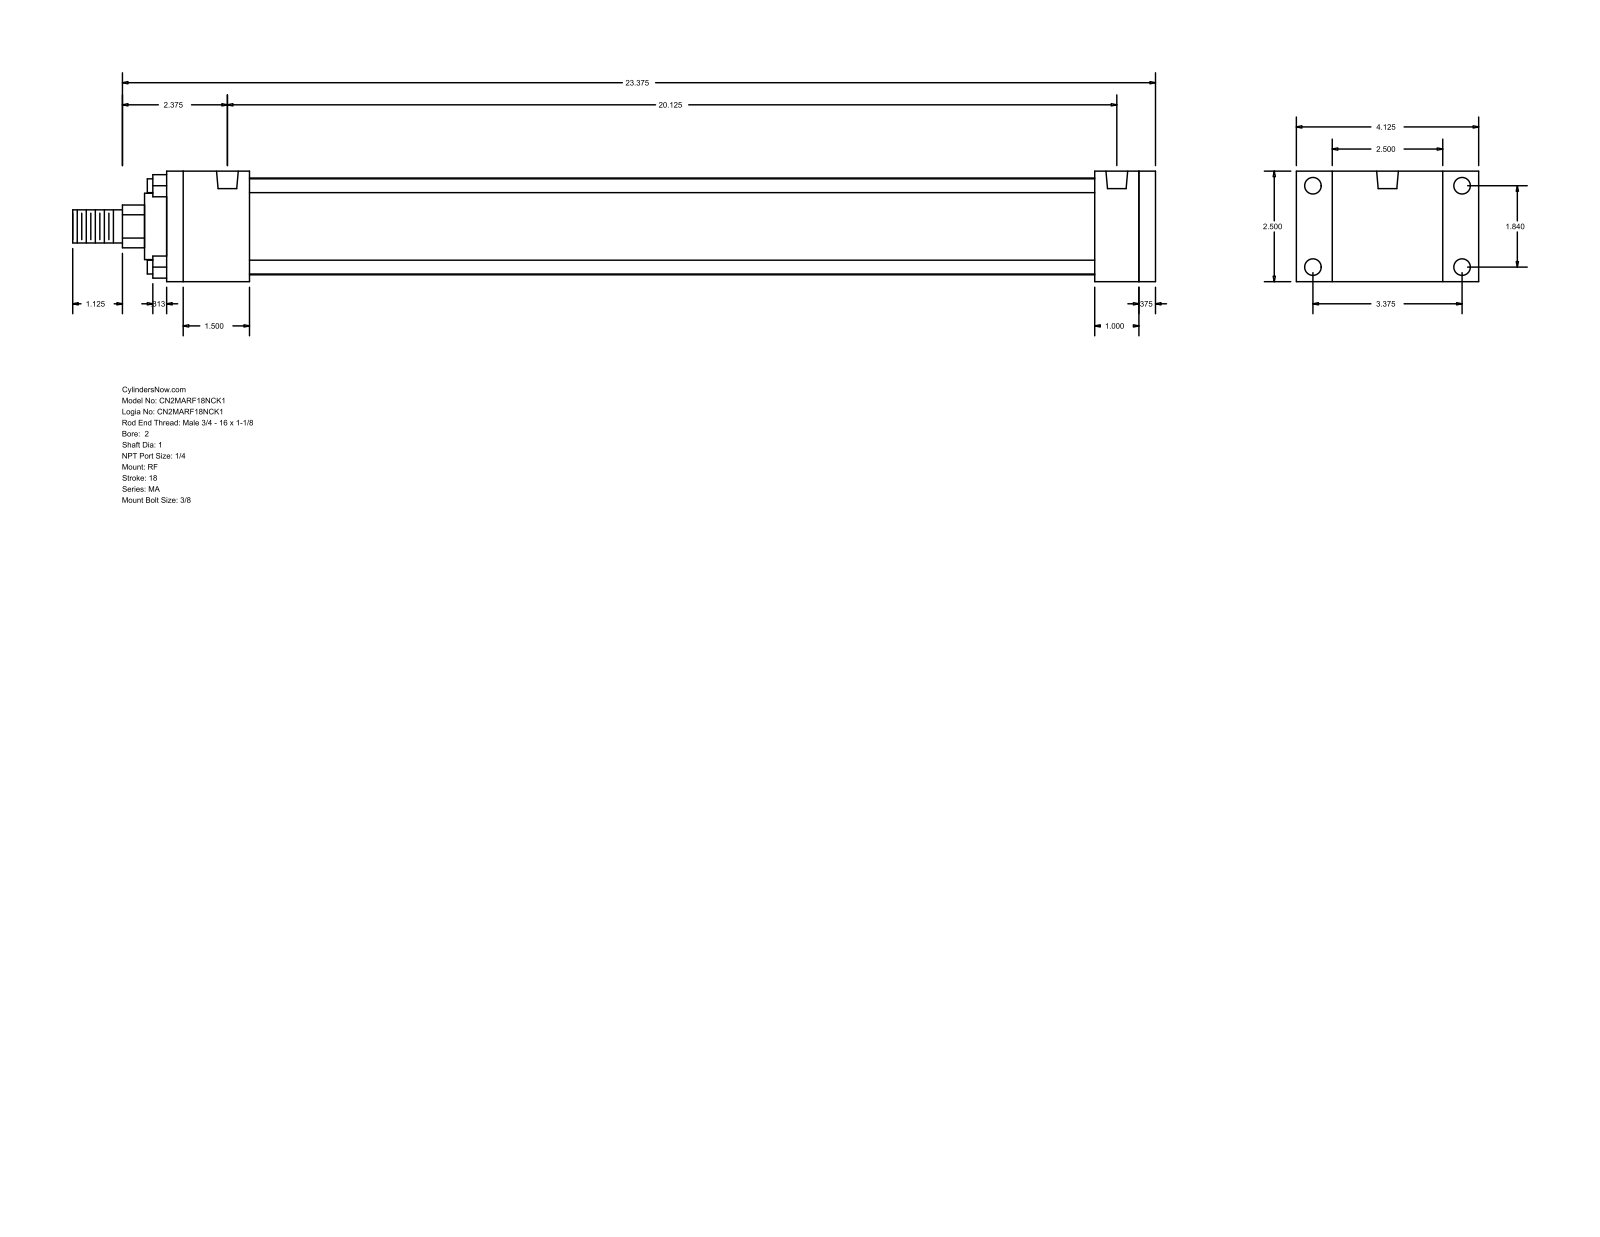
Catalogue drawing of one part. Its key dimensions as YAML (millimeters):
part_name: "MA_RF__0200_1"
step_written_by: "GSSL Pune (CONFIG_CONTROL_DESIGN)"
units: millimeters
bodies: {solids: 0, faces: 92, planar: 64, cylindrical: 28, other: 0}
overall_size: [622.3, 104.78, 63.5]
round_holes:
  - {diameter: 7.94, count: 4}
  - {diameter: 9.53, count: 4}
  - {diameter: 12.49, count: 2}
round_bosses_or_shafts:
  - {diameter: 7.94, count: 4}
  - {diameter: 55.63, count: 1}
  - {diameter: 38.1, count: 1}
  - {diameter: 25.4, count: 1}
  - {diameter: 19.05, count: 1}
partial_cylinders:
  - {radius: 12.29, count: 1}
face_to_face_distances: [63.5, 558.8, 9.53, 568.33, 25.4, 20.64, 12.7, 47.63, 511.17, 520.7]
hole_center_spacings: [46.74, 85.72, 97.63, 511.17]
